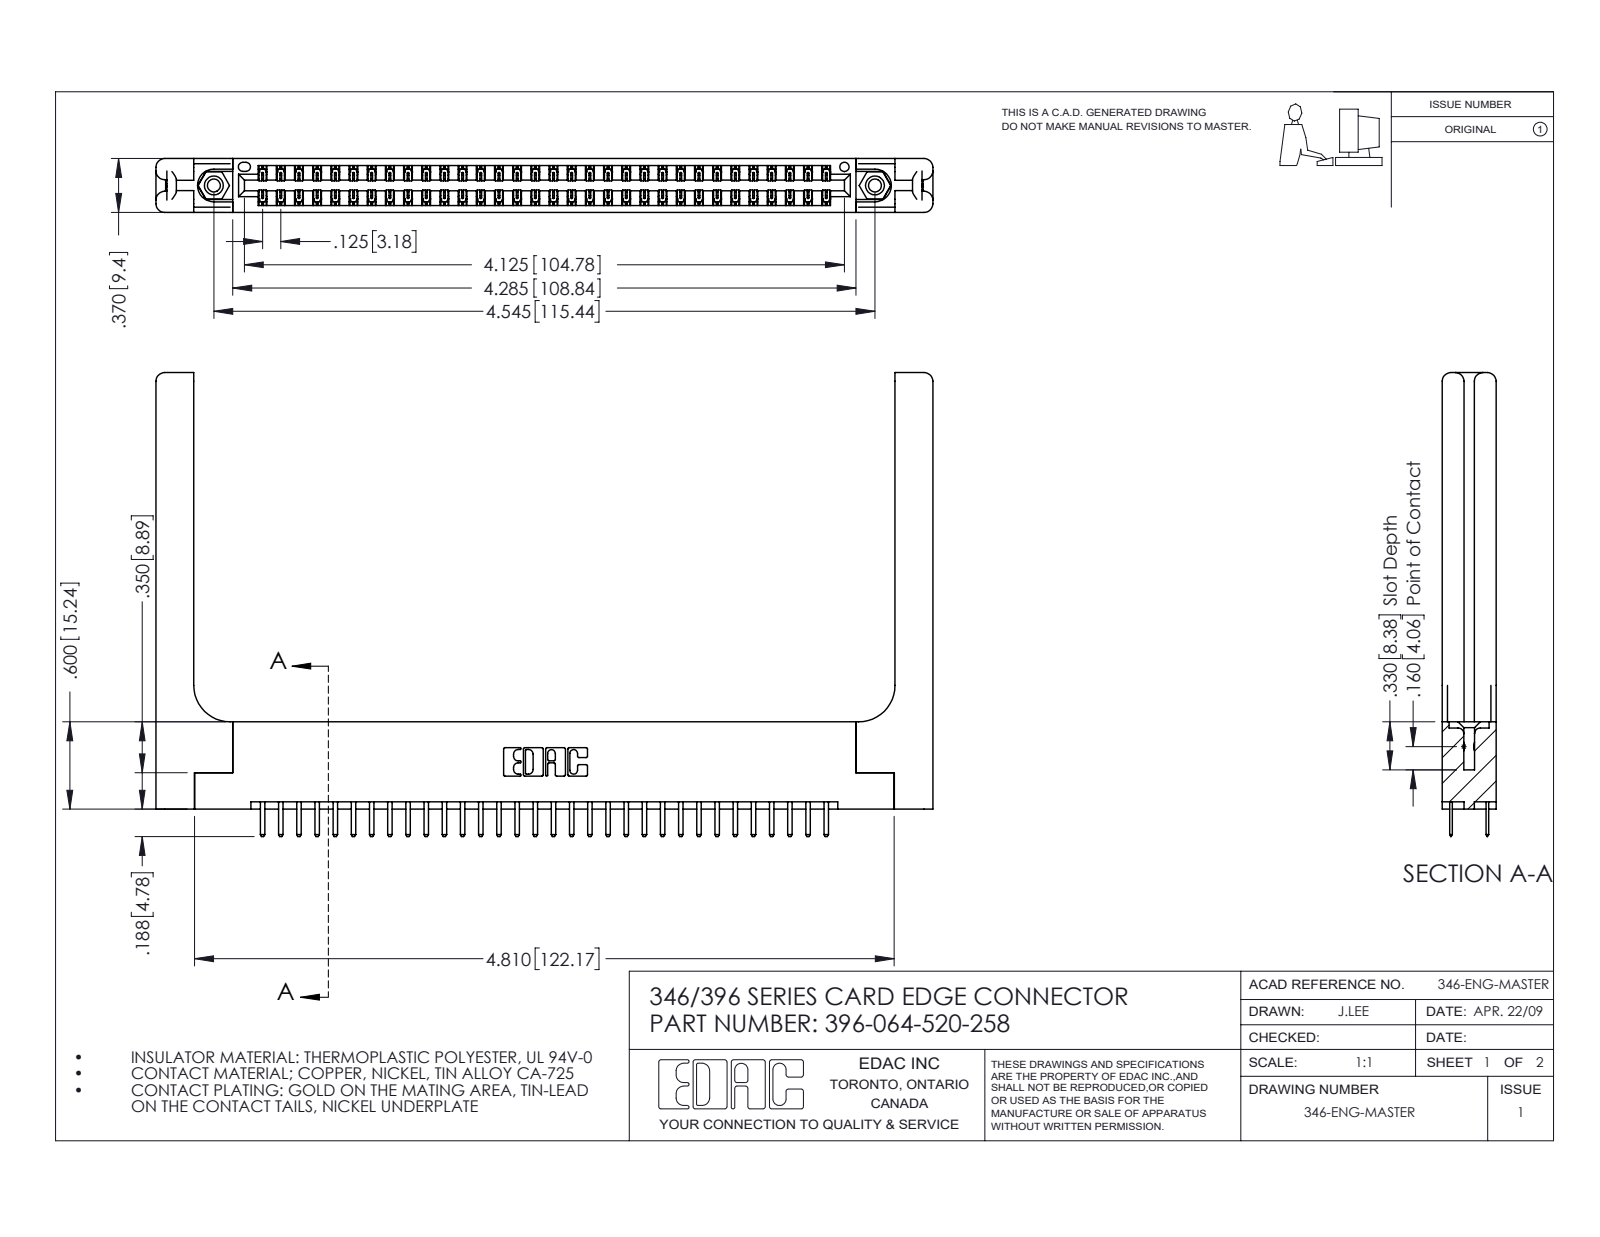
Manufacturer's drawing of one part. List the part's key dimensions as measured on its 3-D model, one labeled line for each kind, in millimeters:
Part name (STEP PRODUCT): 345-250-001_345-250-001-102; 396-064-520-258; 345-292-001_345-293-120; 346-220-058_345-220-058 (+1 more)
STEP written by: SolidWorks 2016 (CONFIG_CONTROL_DESIGN)
Units: millimetres
Bodies: 69 solids, 3962 faces (2592 planar, 1310 cylindrical, 60 other)
Overall size (bounding box): 135.7 × 81 × 9.4
Volume: 20 610 mm³ · Surface area: 22 790 mm²
Round holes (diameter × count): ⌀2.3 ×2, ⌀3.2 ×2, ⌀4 ×2, ⌀1.6 ×1
Round bosses / shafts (diameter × count): ⌀3.9 ×2
Partial cylindrical surfaces — rounded edges, fillets, slot ends (radius × count): R0.2 ×96, R0.3 ×68, R0.3 ×22, R1.5 ×16, R0.2 ×6, R0.8 ×6, R0.7 ×3, R0.4 ×2
Main face-to-face distances: 9.4, 1.2, 8.2, 1.8, 6.4, 3.8, 3.8, 7.6, 0.6, 7
Hole centre spacings: 6.2, 110.2, 115.4
